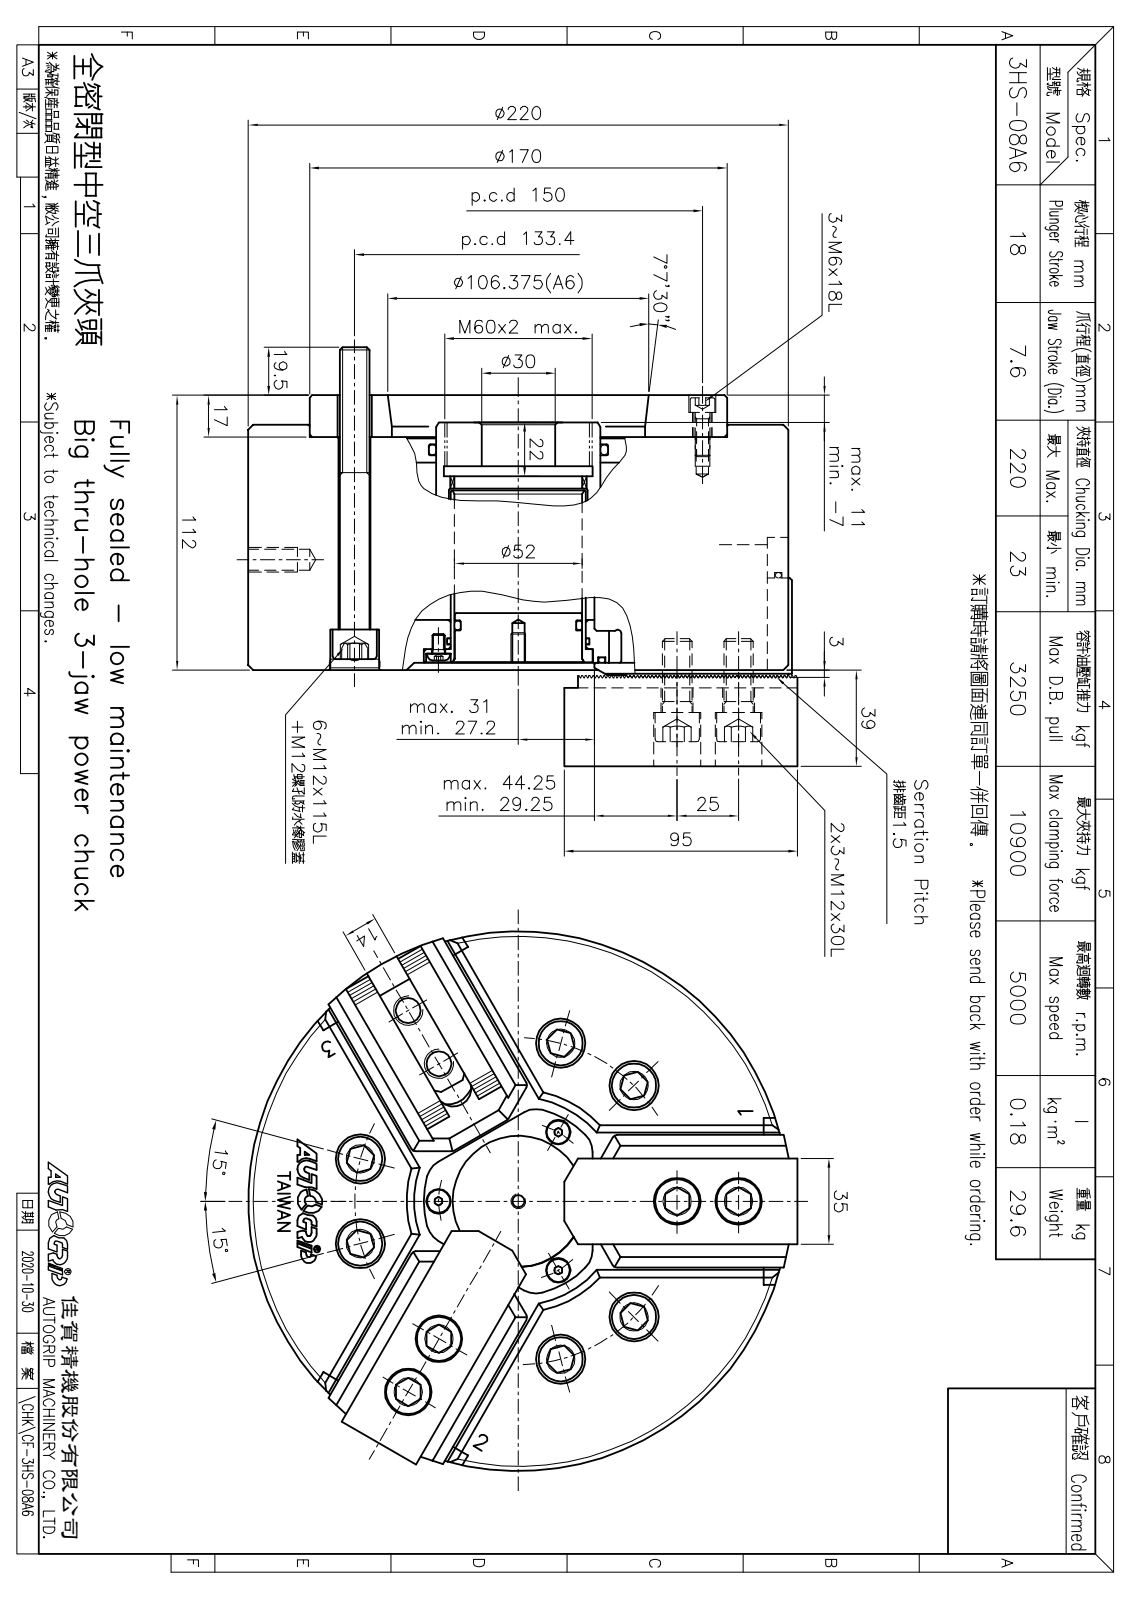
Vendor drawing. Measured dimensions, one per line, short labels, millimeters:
name: CF-3HS-08A6; SJ-08; 圓頭內六角螺栓_M12x30; CF-3HS-08-07000 (+8 more)
written by: SolidWorks 2020 (CONFIG_CONTROL_DESIGN)
unit: mm
bodies: 36 solids, 3168 faces (2118 planar, 833 cylindrical, 217 other)
size: 223.75 × 220 × 170.75
volume: 4 141 000 mm³; area: 571 315 mm²
holes: 12× ⌀14, 8× ⌀11, 6× ⌀4, 6× ⌀5, 6× ⌀6.6, 6× ⌀10.2, 6× ⌀13.5, 6× ⌀20, 4× ⌀13, 4× ⌀19, 3× ⌀19.5, 1× ⌀8.5
bosses: 10× ⌀18, 10× ⌀12, 6× ⌀20.5, 6× ⌀10.5, 3× ⌀10, 3× ⌀6, 1× ⌀220, 1× ⌀77
rounds: 263× R0.1, 12× R2, 10× R20, 6× R7.3, 6× R10, 3× R110
face distances: 47, 95, 50, 10, 5, 11.5, 1, 35.5, 35, 21.5
hole spacings: 112.53, 75, 130.95, 66.69, 86.51, 115.53, 20.24, 54.76
